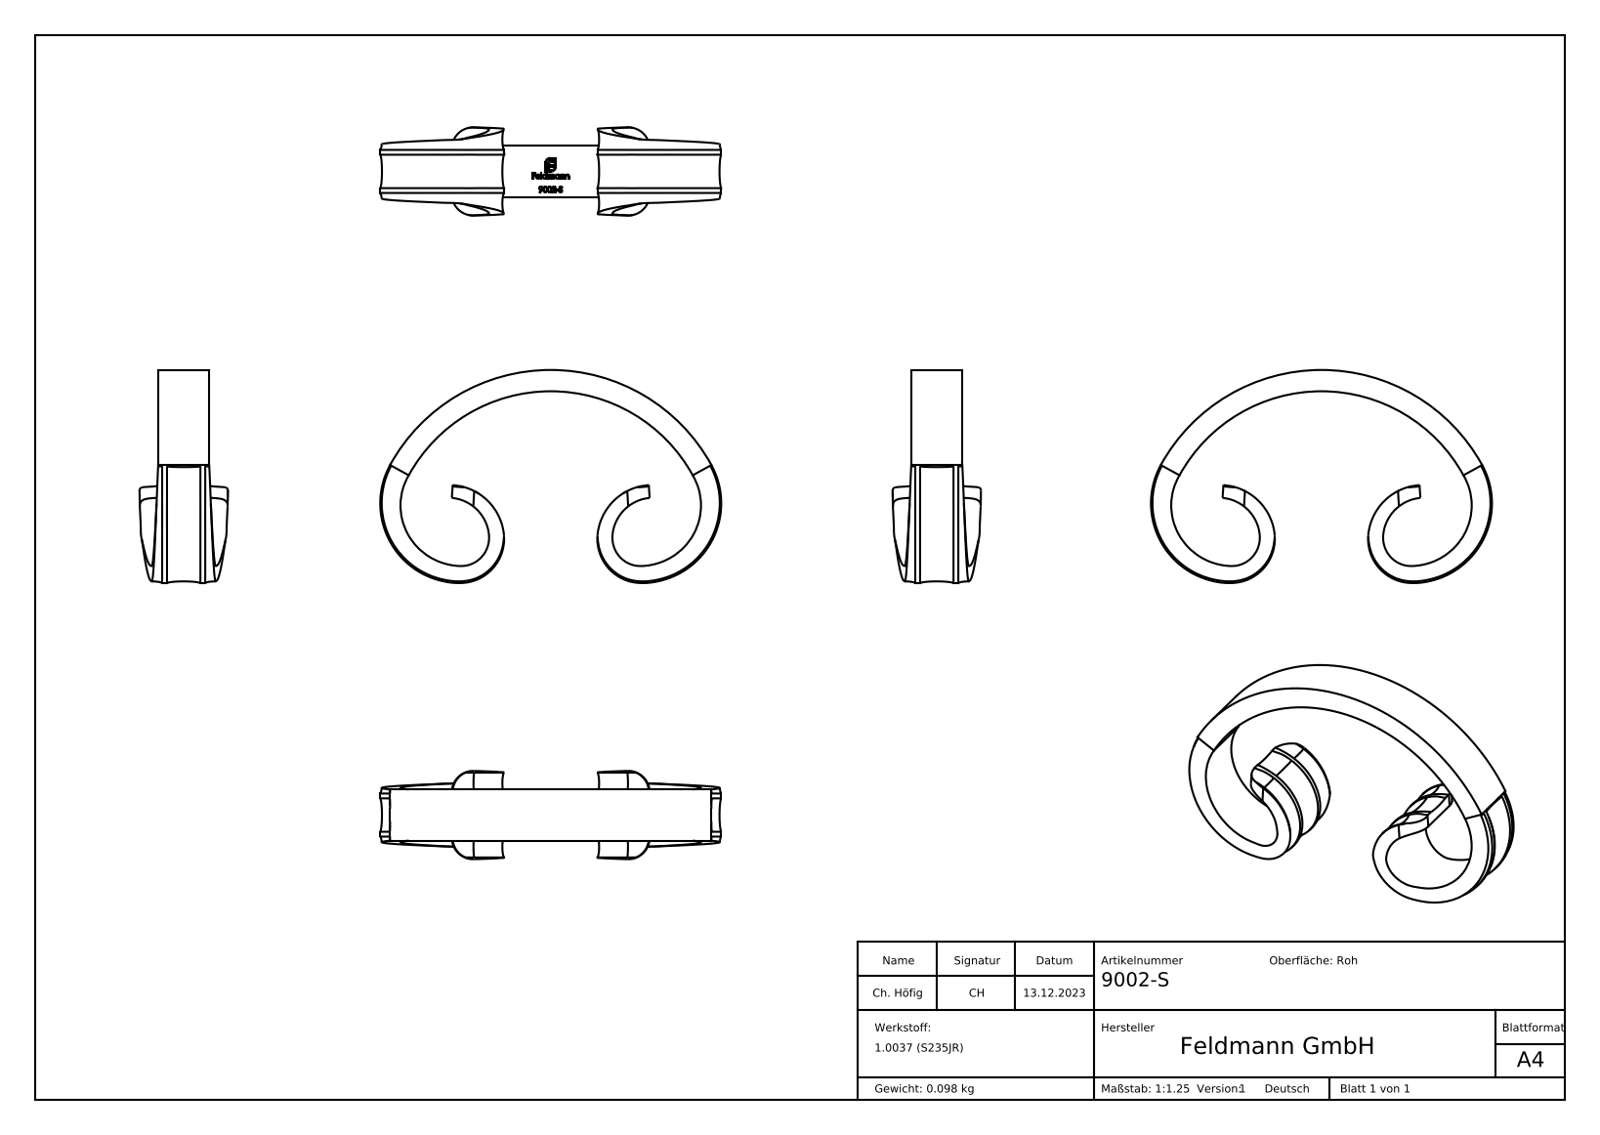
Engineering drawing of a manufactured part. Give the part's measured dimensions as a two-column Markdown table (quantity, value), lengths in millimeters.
| quantity | value |
| --- | --- |
| part name | 9002-S |
| STEP written by | SolidWorks 2018 (CONFIG_CONTROL_DESIGN) |
| units | millimeters |
| bodies | 1 solid, 276 faces (101 planar, 23 cylindrical, 152 other) |
| overall size | 80 × 50 × 20.71 |
| volume | 12 625 mm³ |
| surface area | 8 086 mm² |
| partial cylindrical surfaces (radius × count) | 38 × 1, 38.1 × 1, 43 × 1 |
| main face-to-face distances | 12, 0.58, 0.34, 1.25, 0.39, 1.84, 3.1, 2.85, 2.97, 1.37 |
